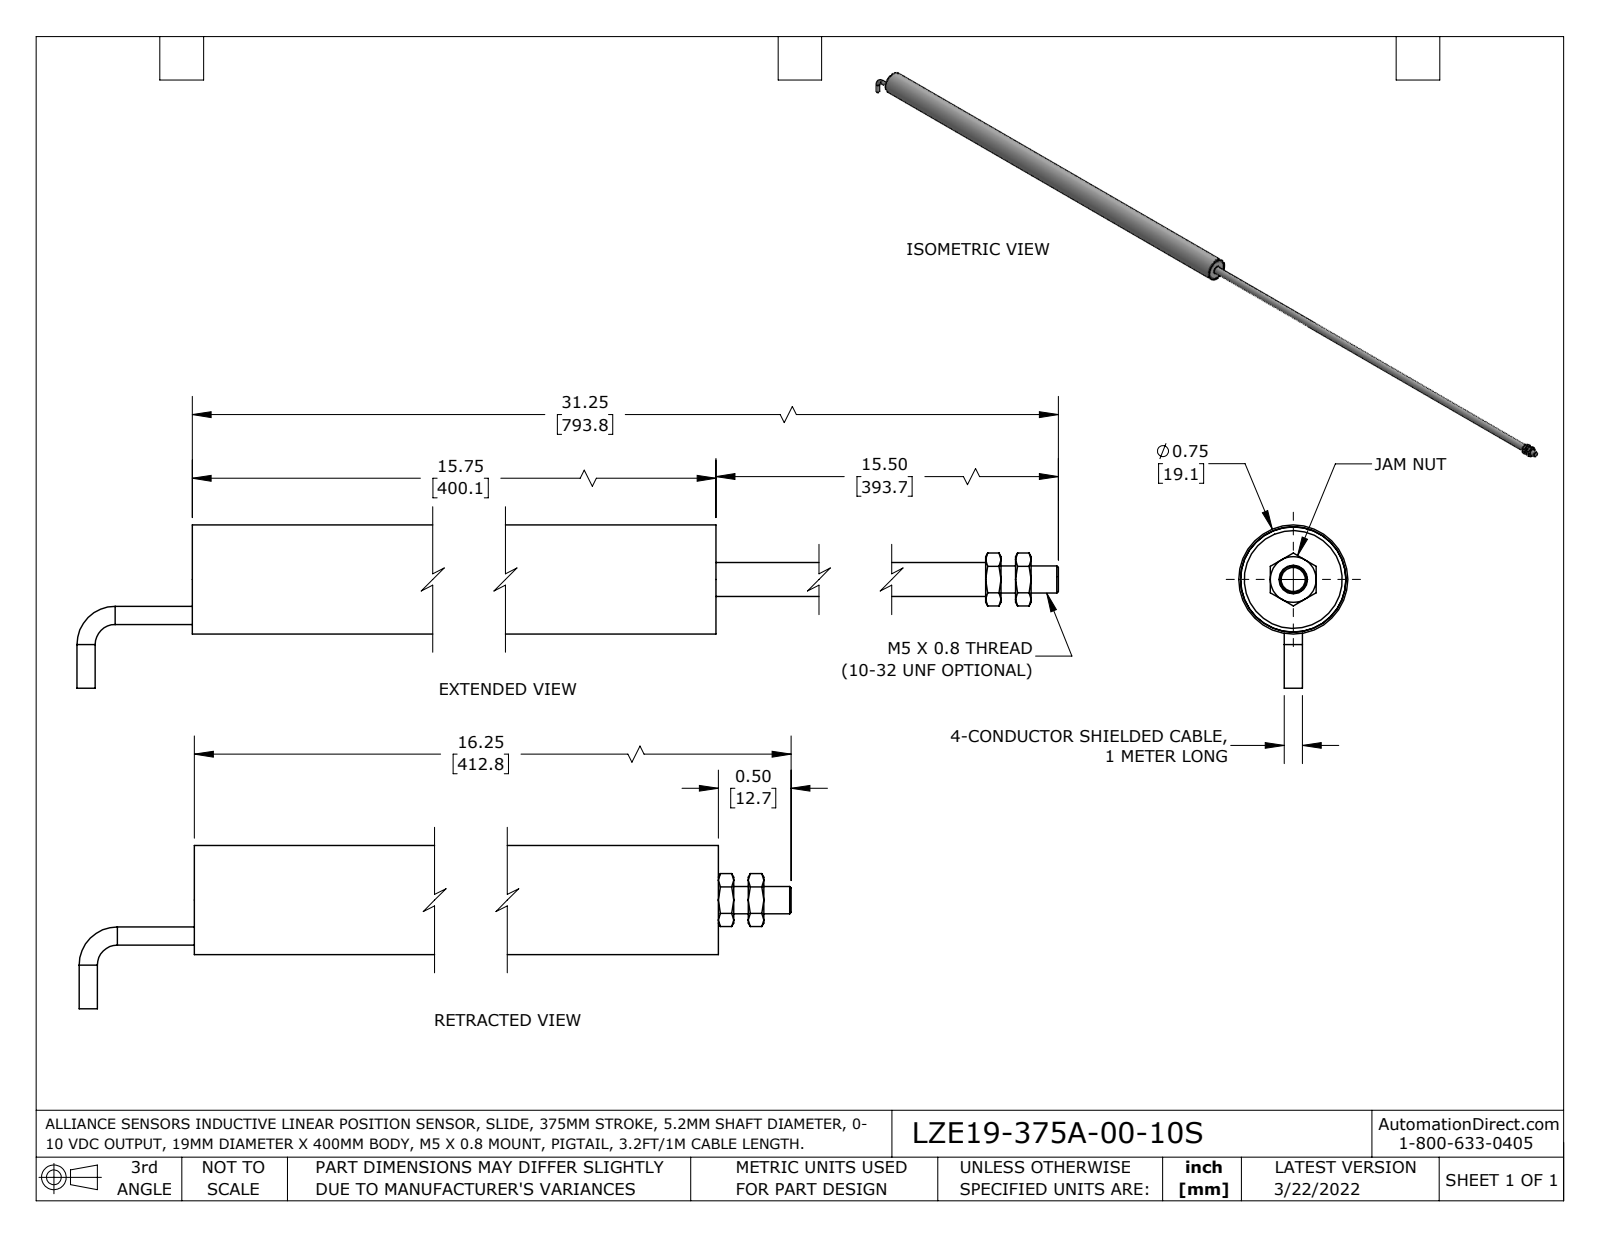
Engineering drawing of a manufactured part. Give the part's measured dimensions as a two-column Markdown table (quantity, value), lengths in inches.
| quantity | value |
| --- | --- |
| part name | 3120-0007-ZY_with slot; 5300-0002; 3120-0008-06_-15; 3120-0006-06_-15-0Y (+6 more) |
| STEP written by | SolidWorks 2021 (AUTOMOTIVE_DESIGN) |
| units | inches |
| bodies | 10 solids, 137 faces (42 planar, 44 cylindrical, 51 other) |
| overall size | 32.043 × 1.121 × 0.75 |
| volume | 2.299 in³ |
| surface area | 130.7 in² |
| round holes (diameter × count) | 0.165 × 1, 0.188 × 1, 0.197 × 1, 0.234 × 1, 0.281 × 1, 0.68 × 1, 0.725 × 1 |
| round bosses / shafts (diameter × count) | 0.125 × 2, 0.75 × 1, 0.723 × 1, 0.278 × 1, 0.187 × 1 |
| partial cylindrical surfaces (radius × count) | 0.052 × 1 |
| main face-to-face distances | 0.06, 15.67, 0.08, 15.61, 15.73, 0.315, 0.374, 0.03, 0.344, 30.74 |
